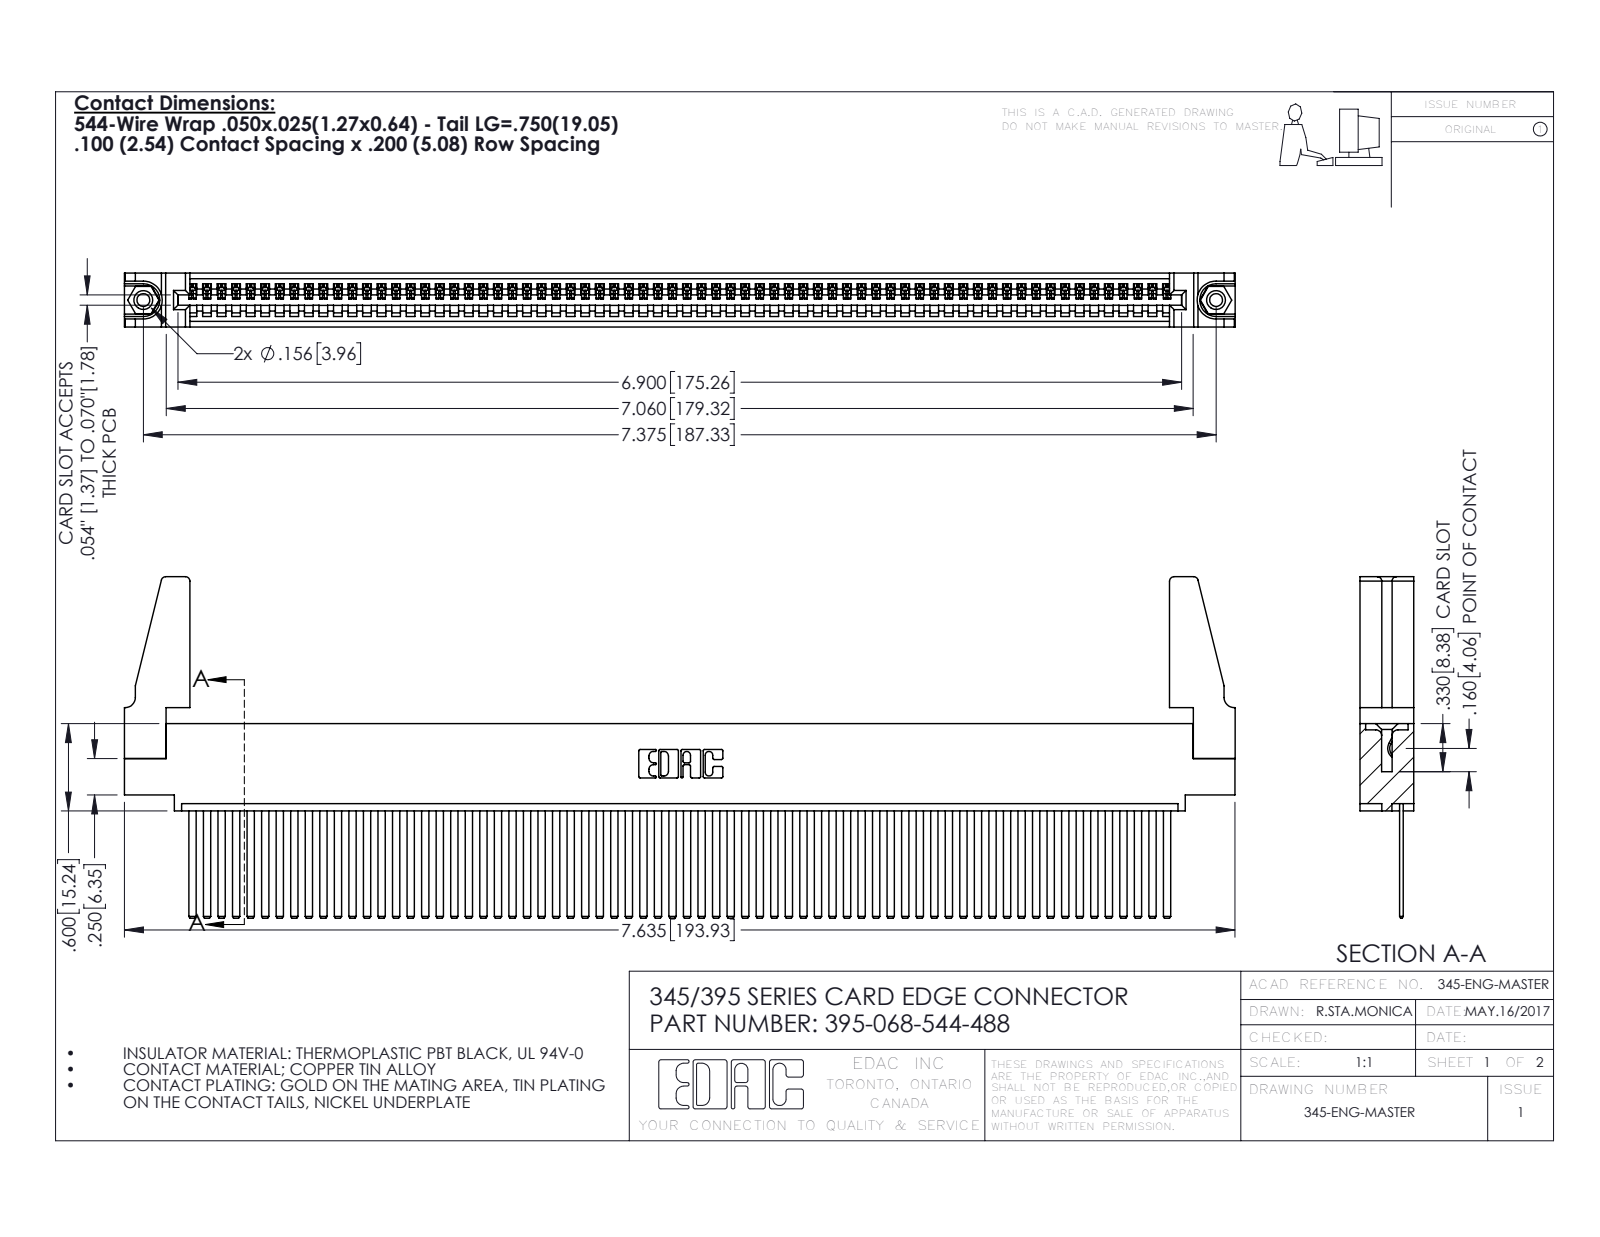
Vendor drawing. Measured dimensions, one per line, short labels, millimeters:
name: 345-220-078_345-220-088; 345-292-001_345-293-144; 395-068-544-488; 345 Part_0.110 Offset - 0.156 Dia-TH (+1 more)
written by: SolidWorks 2016 (CONFIG_CONTROL_DESIGN)
unit: mm
bodies: 73 solids, 3790 faces (2604 planar, 1170 cylindrical, 16 other)
size: 194 × 59.6 × 9.4
volume: 22 600 mm³; area: 31 650 mm²
holes: 2× ⌀2.3, 2× ⌀3.2, 2× ⌀4, 1× ⌀1.6
bosses: 2× ⌀3.9
rounds: 136× R0.2, 22× R0.3, 8× R0.8, 6× R0.2, 6× R0.8, 3× R0.7, 2× R0.8, 2× R1
face distances: 1.8, 7.6, 2.5, 6.9, 0.6, 9.4, 5.1, 5.7, 3.8, 1.8
hole spacings: 6.9, 181.3, 187.3
